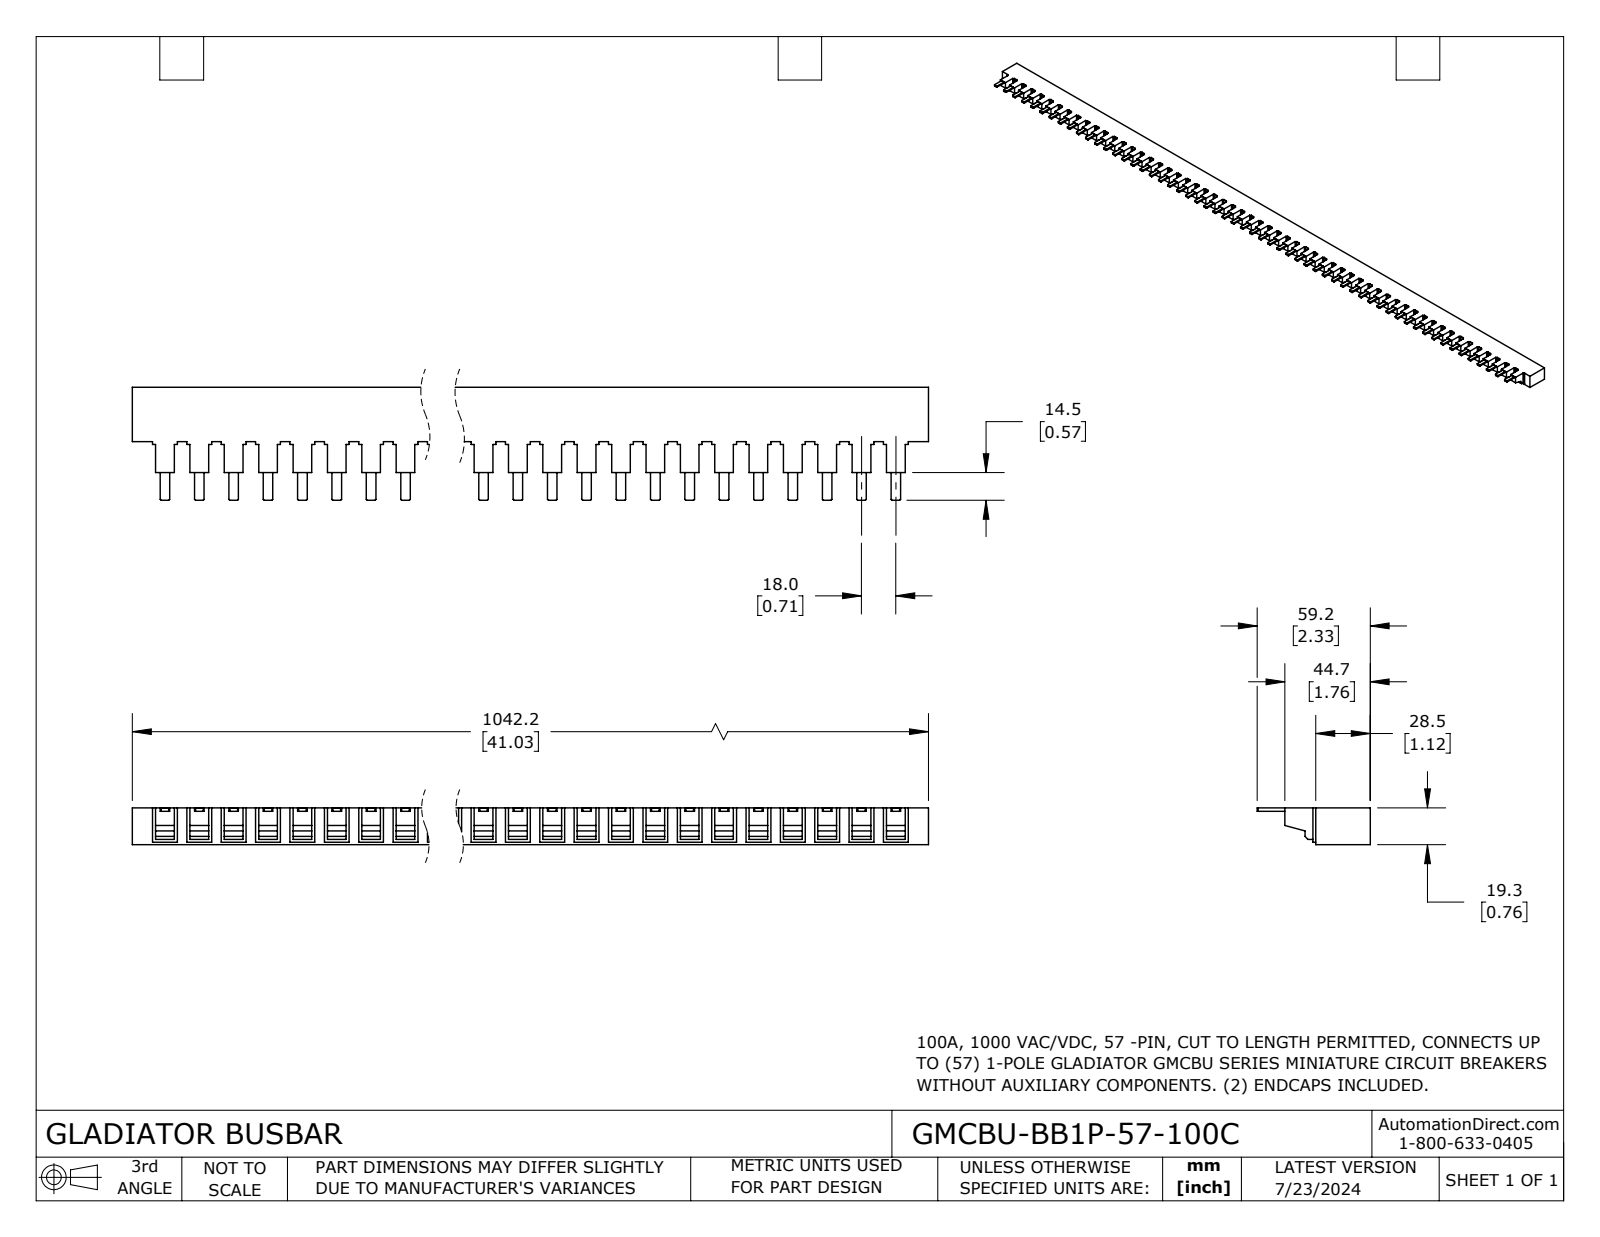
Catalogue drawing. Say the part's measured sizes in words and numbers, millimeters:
The part is named "GMCBU-BB1P-57-100C". Its 3-D file was written by "SolidWorks 2023 (CONFIG_CONTROL_DESIGN)". It is 1 solid with 1032 faces: 1032 planar, 0 cylindrical and 0 other. Overall it measures 1042.2 by 59.2 by 19.3 millimeters. Its volume is 701 200 cubic millimeters and its surface area 152 300 square millimeters. The main face-to-face distances are 19.3, 28.5, 1.5, 44.7, 16.2, 18, 30, 14.7, 1.8, 17.5.
